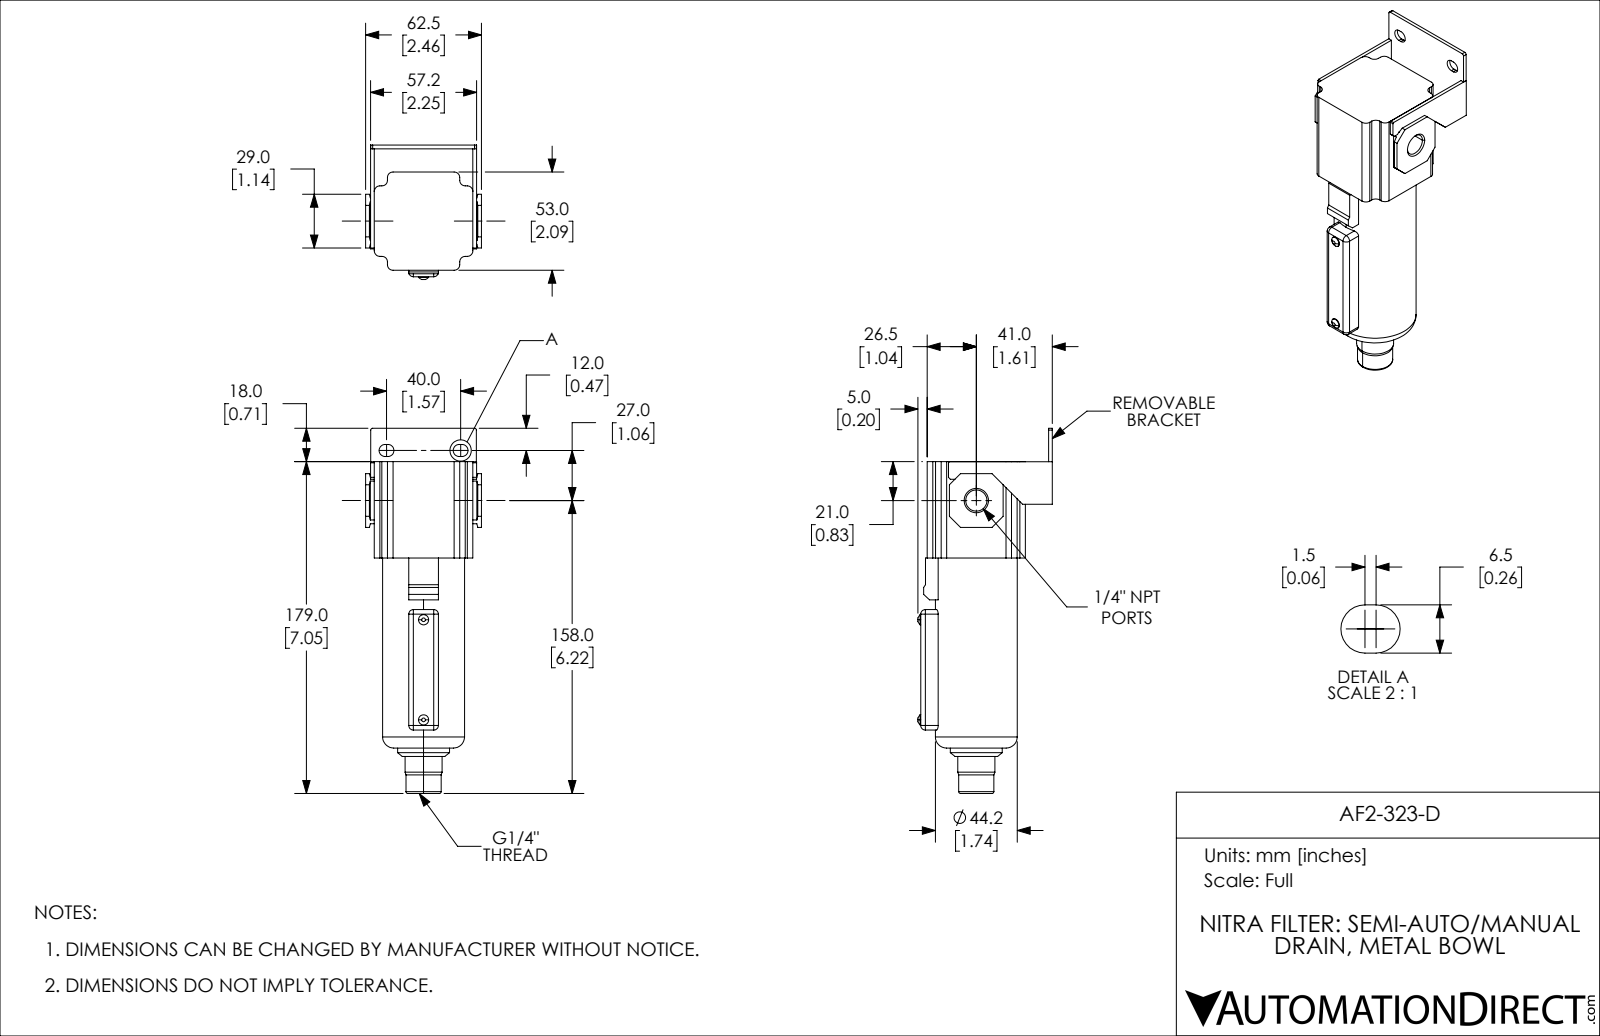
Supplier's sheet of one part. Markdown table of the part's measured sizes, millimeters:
| quantity | value |
| --- | --- |
| part name | AF2-323-D |
| STEP written by | SolidWorks 2019 (CONFIG_CONTROL_DESIGN) |
| units | millimeters |
| bodies | 1 solid, 161 faces (95 planar, 44 cylindrical, 22 other) |
| overall size | 197 × 72.5 × 62.5 |
| volume | 321 429 mm³ |
| surface area | 42 034 mm² |
| round holes (diameter × count) | 8.57 × 1, 11.45 × 1 |
| round bosses / shafts (diameter × count) | 5.5 × 2, 44.2 × 1, 28 × 1, 20 × 1, 19 × 1 |
| partial cylindrical surfaces (radius × count) | 3 × 12, 2.5 × 8, 3.25 × 4, 1 × 2 |
| main face-to-face distances | 2, 12.5, 14.5, 67.5, 65.5, 53, 55.2, 2.65, 4.65, 57.85 |
